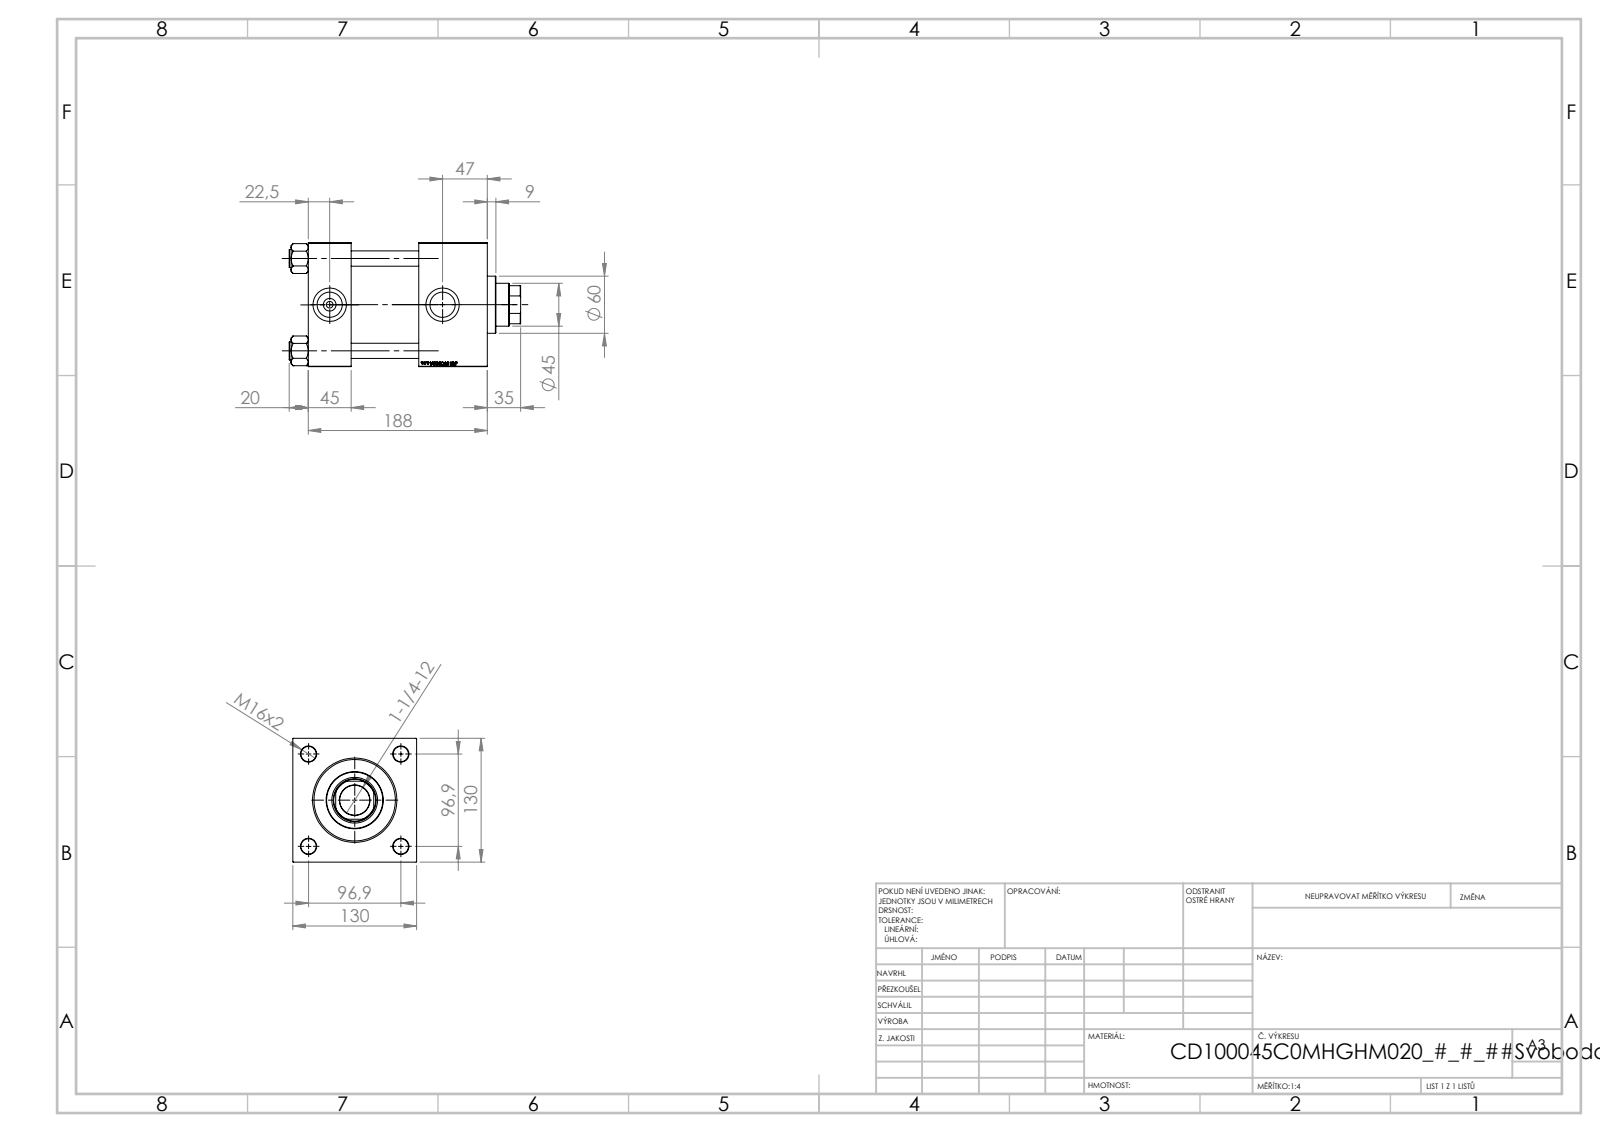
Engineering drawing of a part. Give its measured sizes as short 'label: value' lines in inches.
name: V215CD_Body_C; V215CD_VCP_C; NUT_M5_V215CD_C; V215CD_C_TYCINKA (+1 more)
written by: SolidWorks 2019 (CONFIG_CONTROL_DESIGN)
unit: in
bodies: 11 solids, 1196 faces (574 planar, 86 cylindrical, 536 other)
size: 9.567 × 5.118 × 5.118
volume: 148 in³; area: 505.9 in²
holes: 4× ⌀0.63, 2× ⌀0.276, 2× ⌀1.041, 2× ⌀1.378, 1× ⌀1.24, 1× ⌀1.772, 1× ⌀1.89, 1× ⌀2.992, 1× ⌀3.366, 1× ⌀3.937
bosses: 4× ⌀0.748, 1× ⌀4.173, 1× ⌀2.362
rounds: 1× R0.866
face distances: 5.118, 1.772, 7.402, 5.63, 4.567, 2.795, 2.835, 0.787, 3.78, 2.008
hole spacings: 2.698, 3.815, 5.395, 4.665
